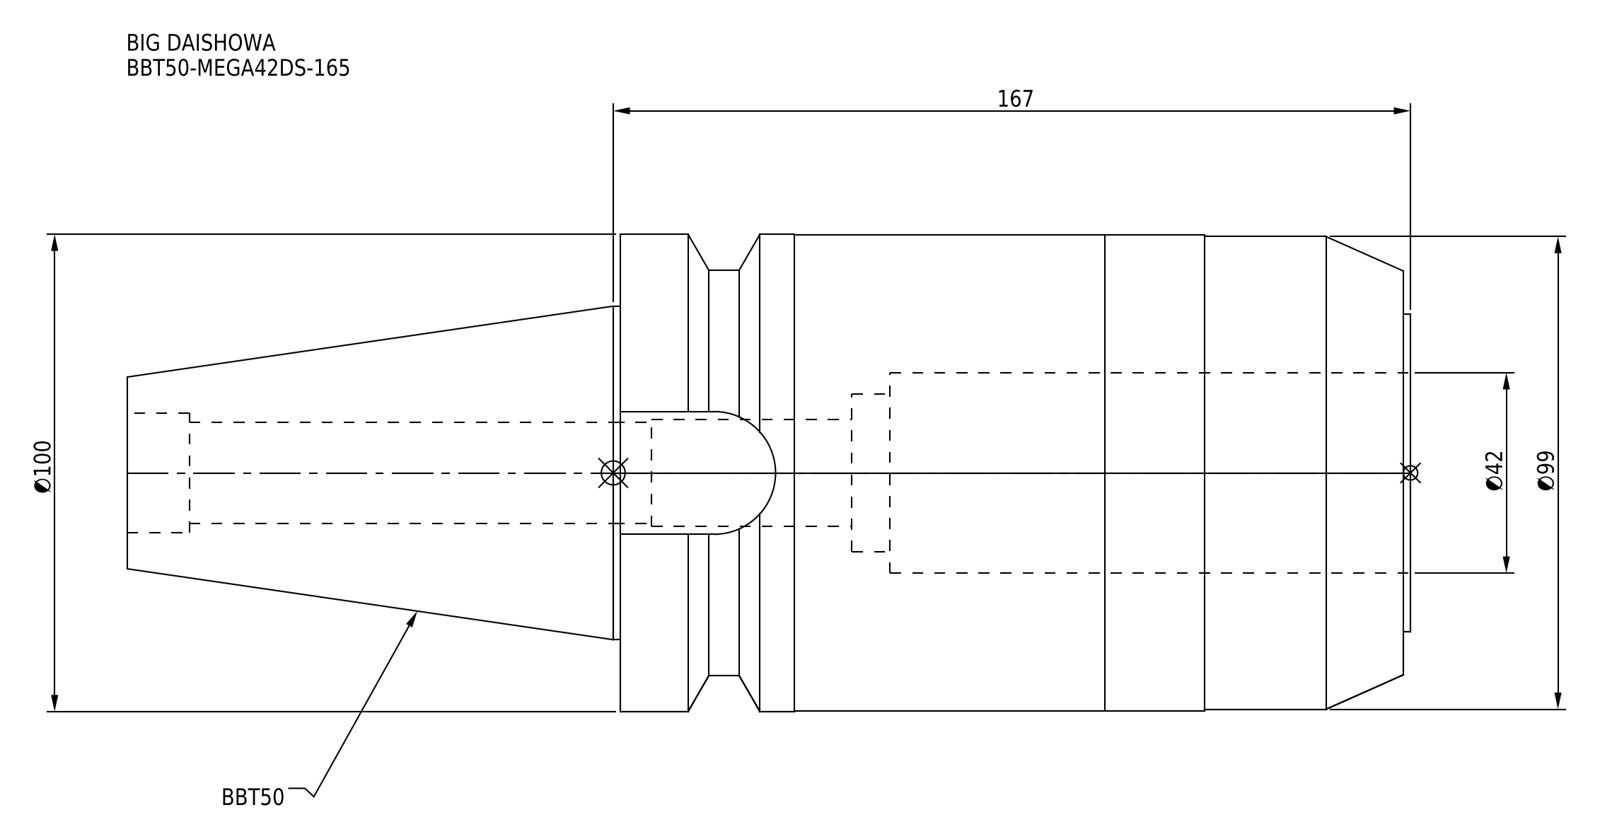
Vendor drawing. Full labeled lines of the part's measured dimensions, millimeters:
Part name (STEP PRODUCT): BBT50-MEGA42DS-165
STEP written by: CREO PARAMETRIC BY PTC INC, 2016380 (AUTOMOTIVE_DESIGN)
Units: millimetres
Bodies: 1 solid, 52 faces (16 planar, 28 cylindrical, 8 other)
Overall size (bounding box): 268.8 × 100 × 100
Volume: 1 263 000 mm³ · Surface area: 108 449 mm²
Round holes (diameter × count): ⌀21.2 ×1, ⌀22.5 ×1, ⌀25 ×1, ⌀33 ×1, ⌀42 ×1
Round bosses / shafts (diameter × count): ⌀100 ×1, ⌀99.7 ×1, ⌀99 ×1, ⌀85 ×1, ⌀69.85 ×1, ⌀66.5 ×1
Partial cylindrical surfaces — rounded edges, fillets, slot ends (radius × count): R12.85 ×1
Main face-to-face distances: 164, 1.5, 165.5, 268.8, 267.3, 103.3, 70.8, 109, 107.5, 56.5
